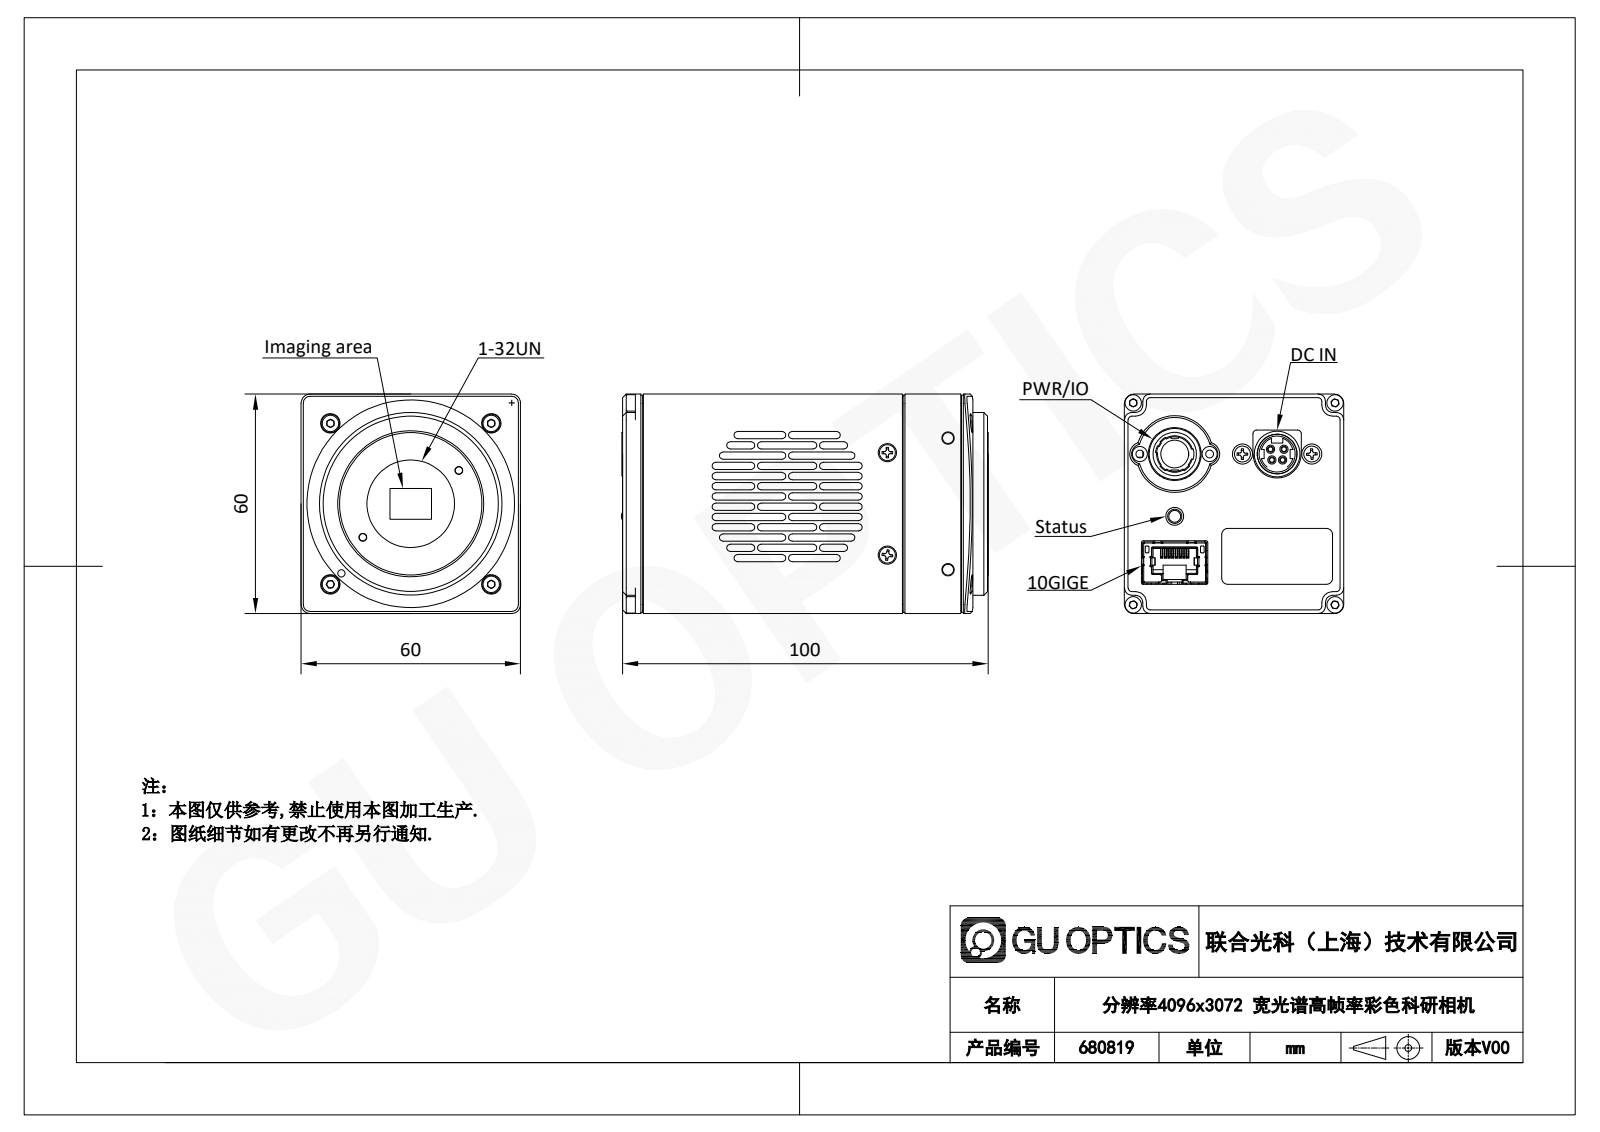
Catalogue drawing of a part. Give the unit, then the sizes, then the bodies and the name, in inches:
Units: inches
Overall size (bounding box): 3.949 × 2.362 × 2.362
Round holes (diameter × count): ⌀0.028 ×25, ⌀0.106 ×14, ⌀0.081 ×8, ⌀0.087 ×8, ⌀0.197 ×8, ⌀0.063 ×7, ⌀0.053 ×4, ⌀0.067 ×4, ⌀0.118 ×4, ⌀0.079 ×3, ⌀0.031 ×2, ⌀0.037 ×2
Round bosses / shafts (diameter × count): ⌀0.024 ×178, ⌀0.098 ×11, ⌀0.177 ×8, ⌀0.063 ×5, ⌀0.079 ×4, ⌀0.173 ×2, ⌀0.157 ×2, ⌀0.15 ×2
Partial cylindrical surfaces — rounded edges, fillets, slot ends (radius × count): R0.039 ×86, R0.008 ×79, R0.012 ×79, R0.079 ×40, R0.02 ×24, R0.016 ×22, R0.01 ×21, R0.059 ×20
Main face-to-face distances: 0.059, 2.303, 2.362, 2.244, 0.079, 0.157, 0.02, 3.611, 0.039, 0.177
Hole centre spacings: 0.066, 0.1, 0.907, 0.156, 0.2, 0.057, 1.896, 1.965
Volume: 4.629 in³ · Surface area: 141.3 in²
Bodies: 38 solids, 6404 faces (4900 planar, 1220 cylindrical, 284 other)
Part name (STEP PRODUCT): 中壳; KPJX-PM-4S_4-1-SOLID1; 2jgmfq000-00060; GB／T819．1-2000十字槽沉头螺钉M1．6×16 (+8 more)
STEP written by: SolidWorks 2024 (CONFIG_CONTROL_DESIGN)
